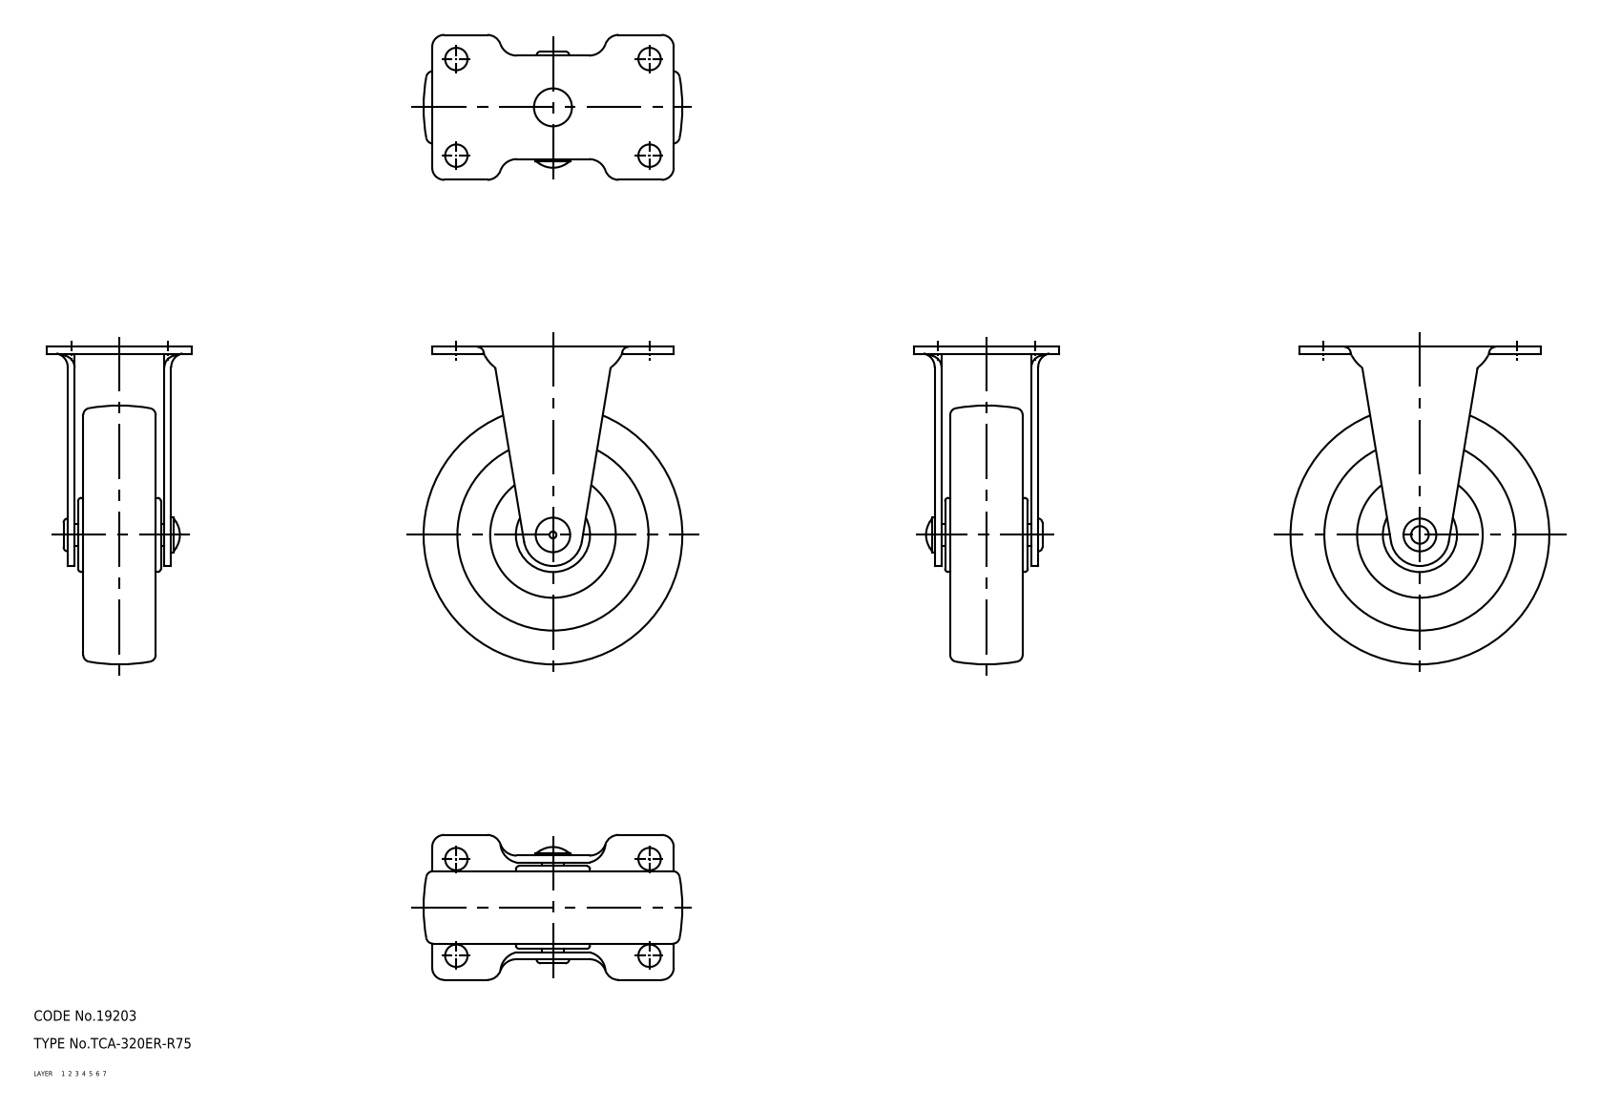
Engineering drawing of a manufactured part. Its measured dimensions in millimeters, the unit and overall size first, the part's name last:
Units: millimetres
Overall size (bounding box): 92 × 75 × 42.07
Volume: 99 247 mm³ · Surface area: 26 513 mm²
Bodies: 3 solids, 141 faces (0 planar, 0 cylindrical, 141 other)
Part name (STEP PRODUCT): wheel; axle; 320ER_R75_3423_36
STEP written by: CADfix (AUTOMOTIVE_DESIGN)
